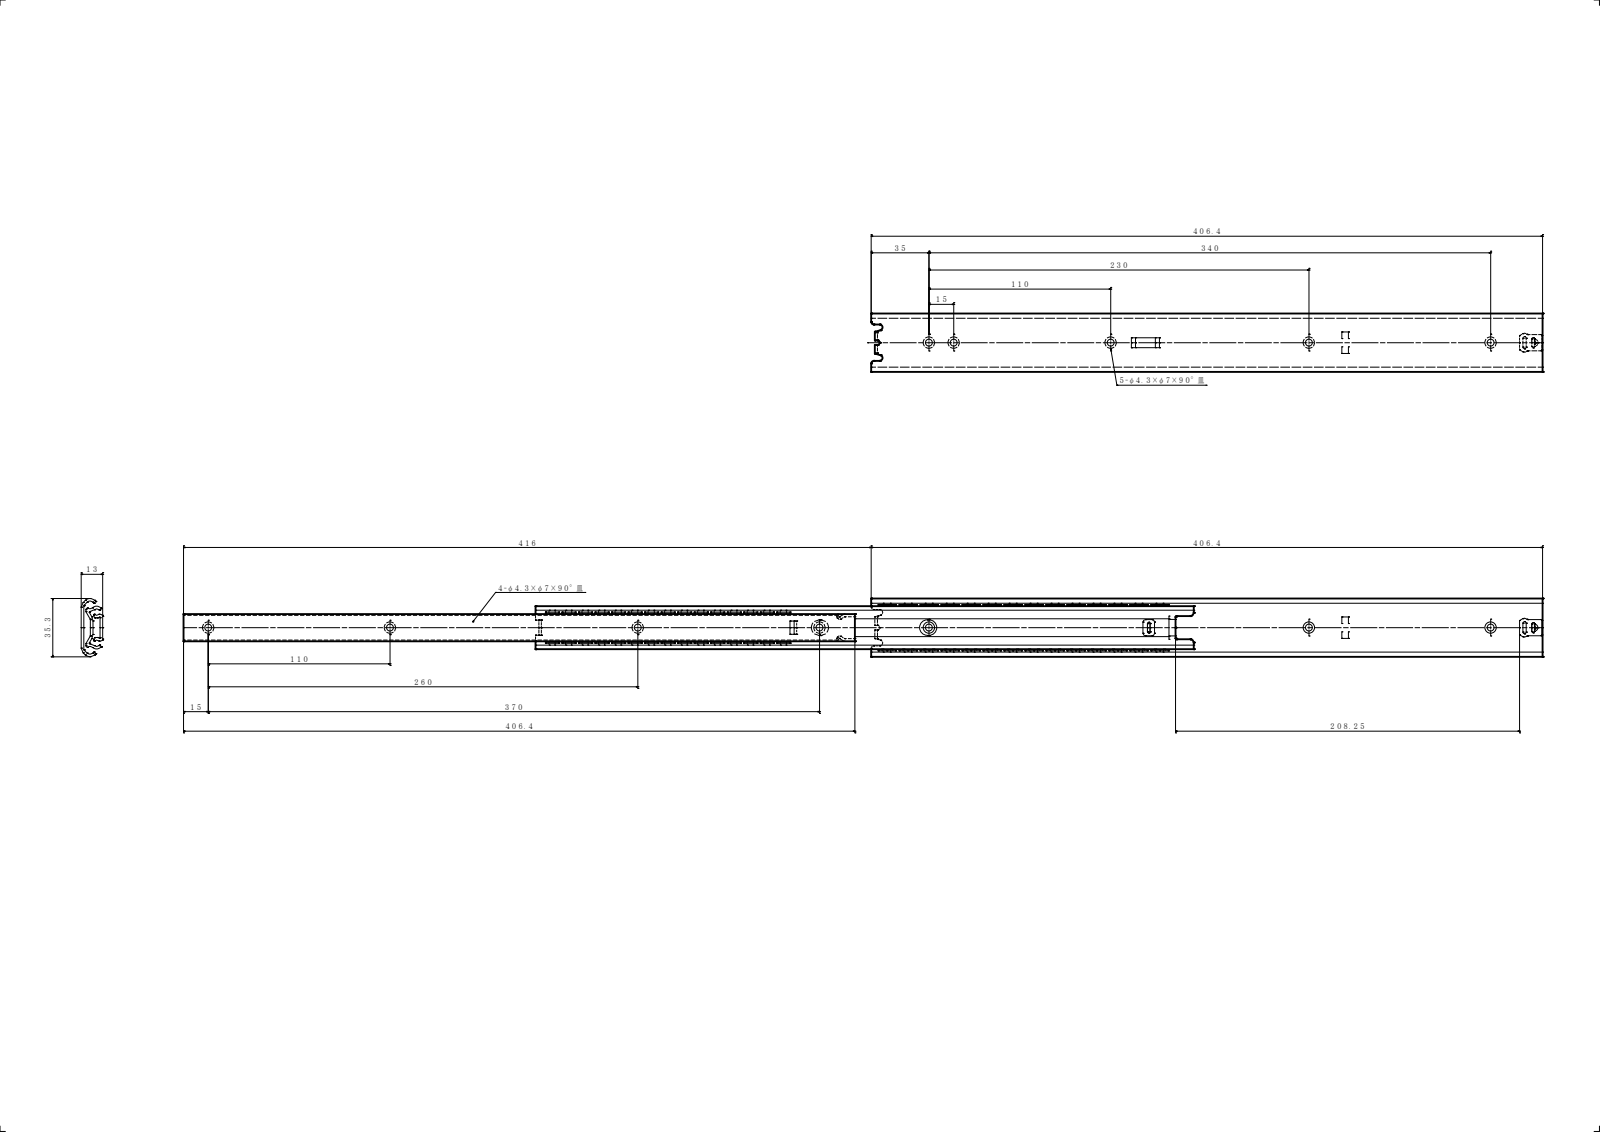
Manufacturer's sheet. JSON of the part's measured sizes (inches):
{"part_name": "PN32; C351-16 CM; C351-16 OM; PN36 (+2 more)", "step_written_by": "SolidWorks 2019 (CONFIG_CONTROL_DESIGN)", "units": "inches", "bodies": {"solids": 5, "faces": 300, "planar": 144, "cylindrical": 136, "other": 20}, "overall_size": [32.389, 1.39, 0.512], "volume_in3": 4.34, "surface_area_in2": 143.2, "round_holes": [[0.169, 9], [0.177, 1]], "partial_cylinders_radius": [[0.02, 21], [0.059, 8], [0.079, 8], [0.118, 8], [0.012, 6], [0.031, 4], [0.039, 4], [0.063, 4]], "face_to_face_distances": [0.063, 0.449, 0.213, 0.236, 0.512, 0.386, 0.15, 0.299, 0.276, 0.173], "hole_center_spacings": [4.331, 6.941, 9.055, 10.236, 15.996, 17.177, 26.232, 0.591]}
